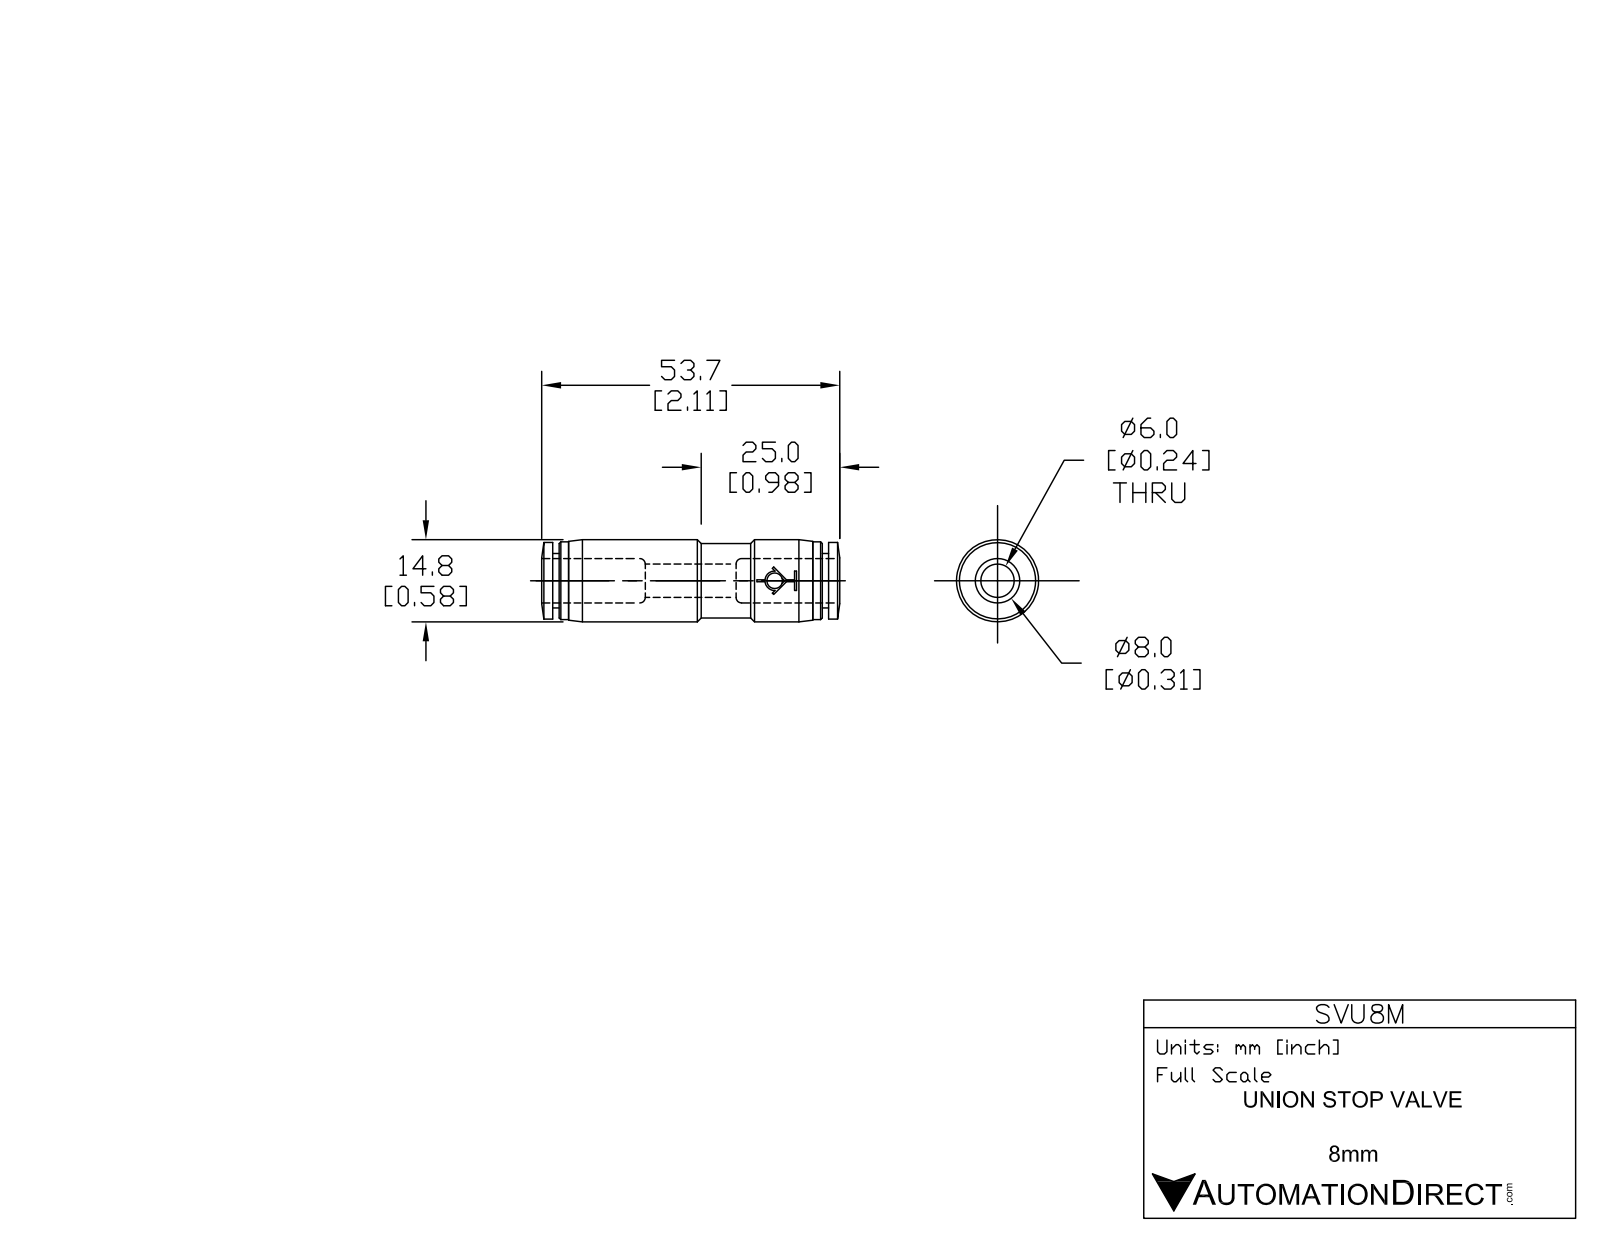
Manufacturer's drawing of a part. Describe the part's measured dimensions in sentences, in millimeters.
The part is named "SVU8M". Its 3-D file was written by "SolidWorks 2015 (AUTOMOTIVE_DESIGN)". It is 1 solid with 76 faces: 26 planar, 30 cylindrical and 20 other. Overall it measures 53.7 by 14.9 by 14.8 millimeters. Its volume is 5 950 cubic millimeters and its surface area 4 221 square millimeters. Round holes: 1 of diameter 2.8, 1 of diameter 6.4, 1 of diameter 8.3. Round bosses or shafts: 1 of diameter 14.8, 1 of diameter 14, 1 of diameter 13.8, 1 of diameter 13.4, 1 of diameter 9.8. Partial cylindrical surfaces (rounded edges, fillets, slot ends): 1 of radius 1.8, 1 of radius 7.5. The main face-to-face distances are 1.1, 48.5, 49.7, 47.4, 16.7, 33, 15.5, 31.9, 16.3, 3.1.
